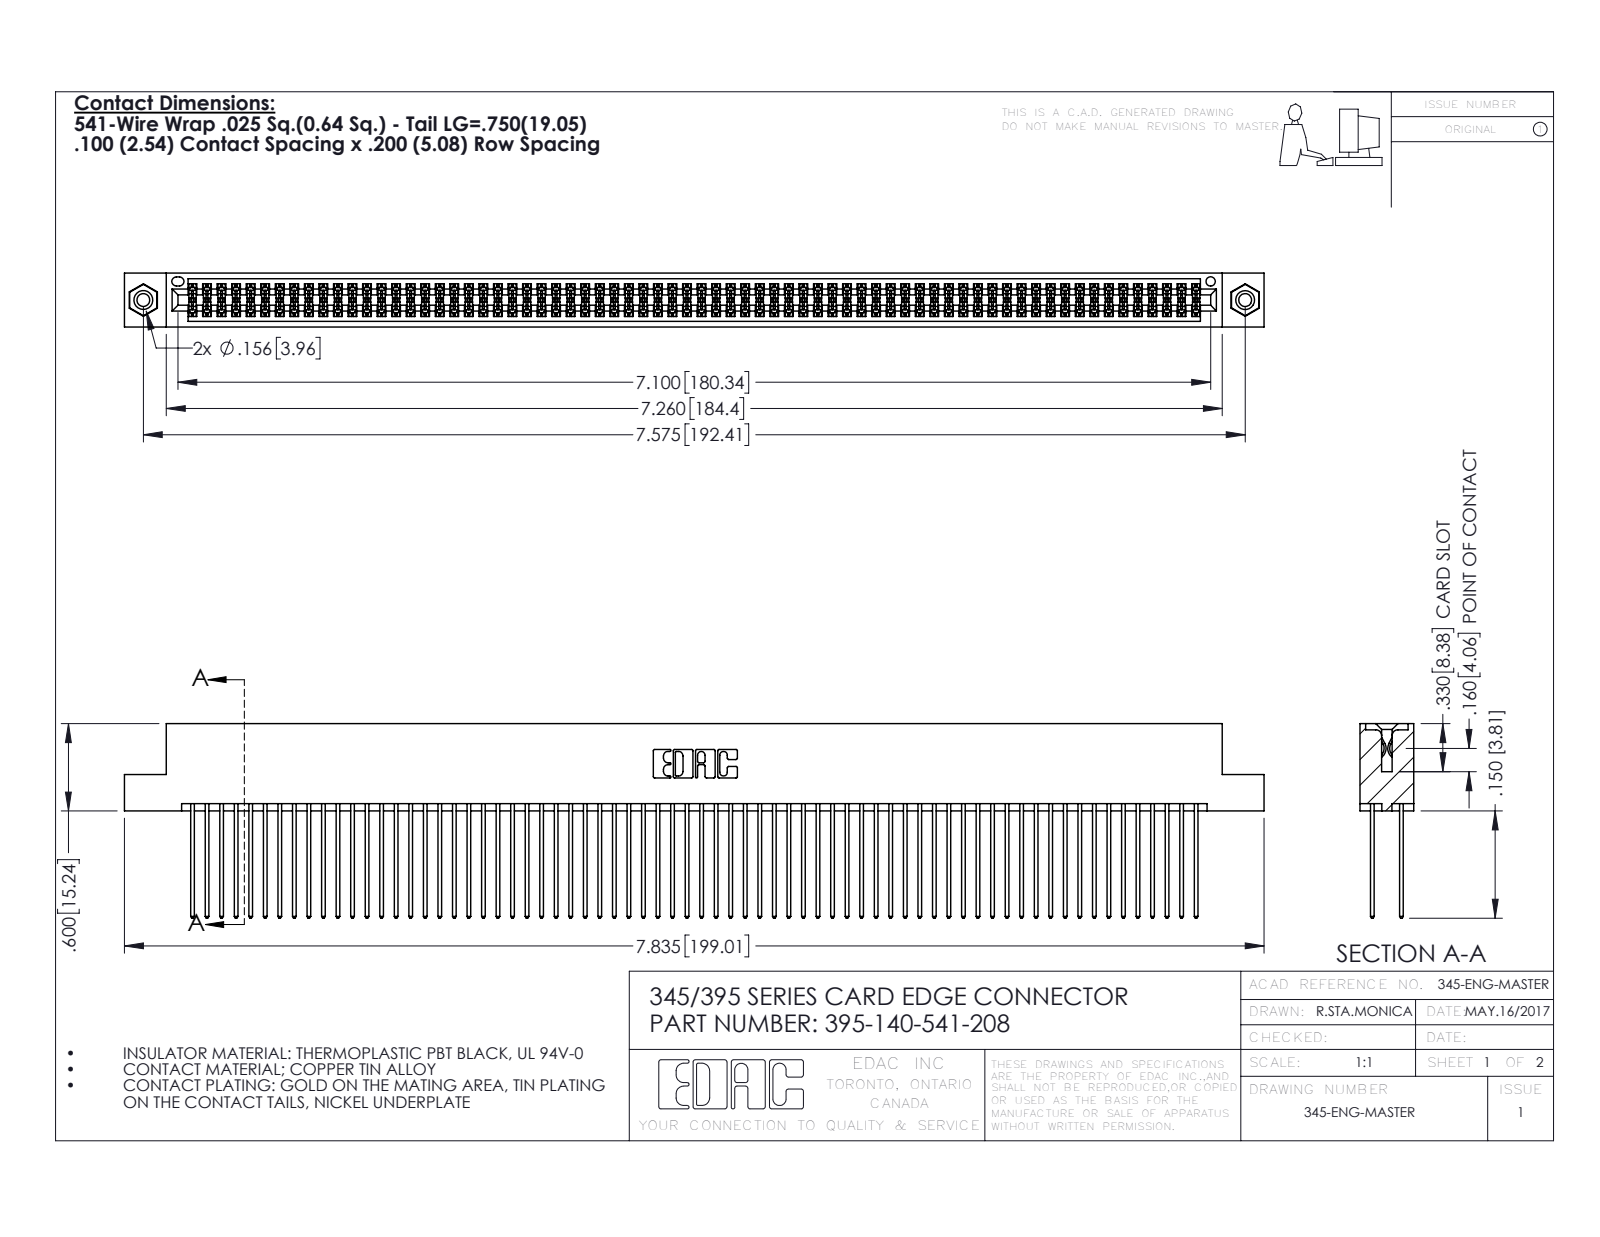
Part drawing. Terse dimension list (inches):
name: 345 Part_Flush Mounting Lugs - 0.156 Dia-TI; 395-140-541-208; 345-250-001_345-250-003-102; 345-292-001_345-293-141
written by: SolidWorks 2016 (CONFIG_CONTROL_DESIGN)
unit: in
bodies: 143 solids, 7186 faces (4732 planar, 2438 cylindrical, 16 other)
size: 7.835 × 1.337 × 0.37
volume: 1.244 in³; area: 53.43 in²
holes: 2× ⌀0.089, 2× ⌀0.125, 2× ⌀0.156, 1× ⌀0.064
bosses: 2× ⌀0.155
rounds: 210× R0.006, 140× R0.01, 22× R0.01, 6× R0.007, 6× R0.031, 3× R0.026, 2× R0.014, 2× R0.019
face distances: 0.072, 0.298, 0.2, 0.098, 0.272, 0.025, 0.225, 0.37, 0.175, 0.149
hole spacings: 0.27, 7.339, 7.575
